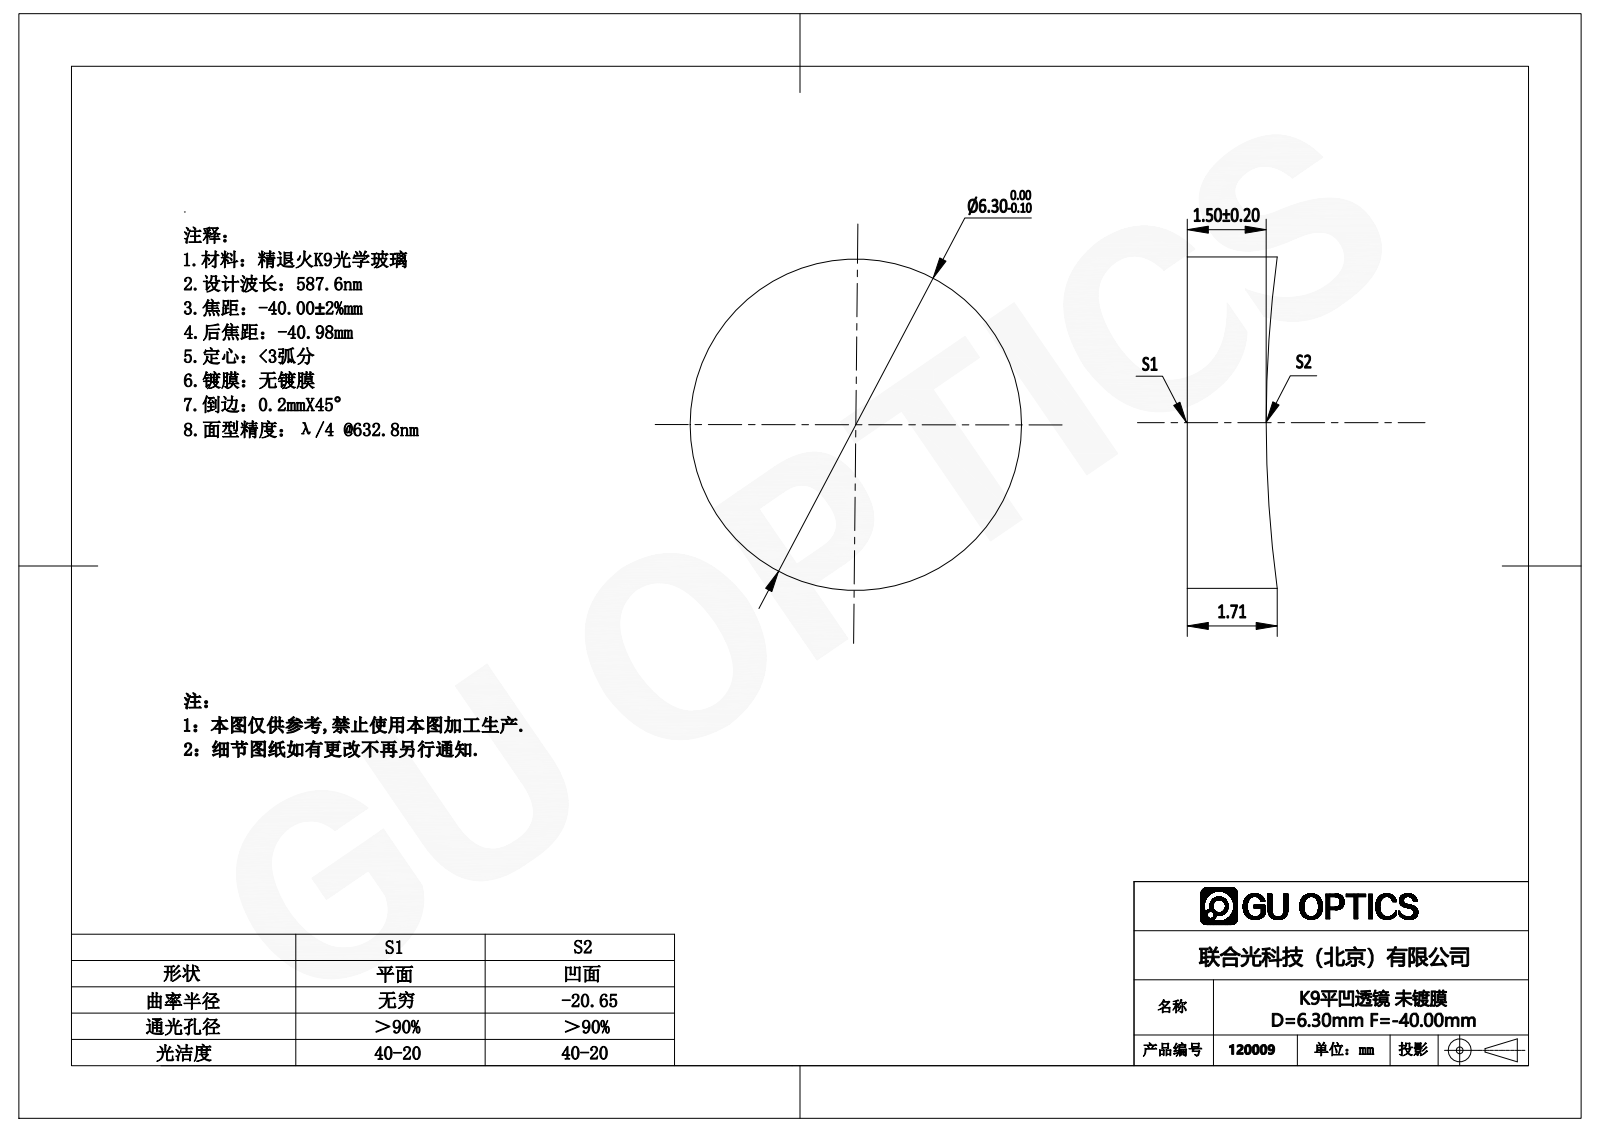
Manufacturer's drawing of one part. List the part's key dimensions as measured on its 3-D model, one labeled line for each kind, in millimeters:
Part name (STEP PRODUCT): 120009
STEP written by: SolidWorks 2016 (AUTOMOTIVE_DESIGN)
Units: millimetres
Bodies: 1 solid, 5 faces (1 planar, 2 cylindrical, 2 other)
Overall size (bounding box): 6.3 × 6.3 × 1.71
Volume: 50 mm³ · Surface area: 96 mm²
Round bosses / shafts (diameter × count): ⌀6.3 ×1
